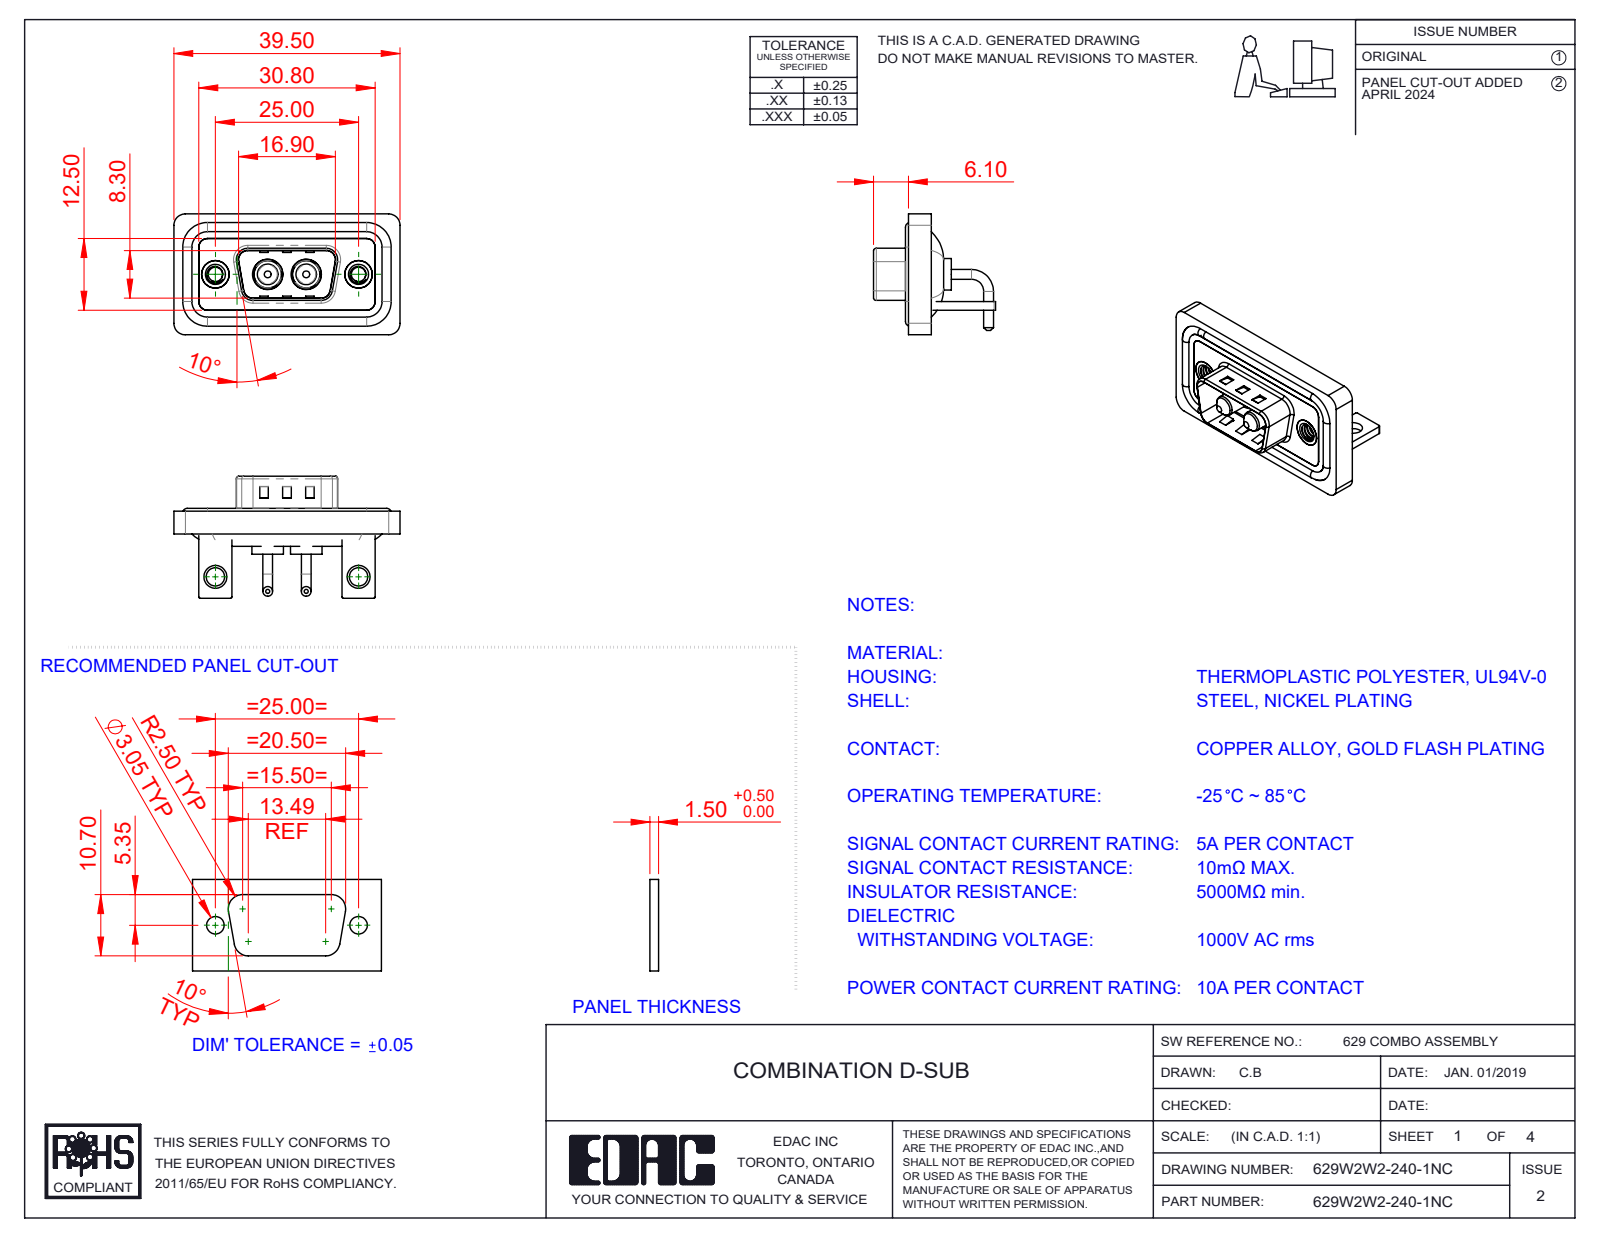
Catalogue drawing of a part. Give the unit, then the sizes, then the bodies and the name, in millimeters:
Units: millimetres
Overall size (bounding box): 39.5 × 21.3 × 21.1
Round holes (diameter × count): ⌀2.5 ×2, ⌀3.2 ×2, ⌀4 ×2, ⌀4.8 ×2, ⌀4.85 ×2, ⌀5 ×2, ⌀5.3 ×2
Round bosses / shafts (diameter × count): ⌀1.7 ×4, ⌀1.6 ×4, ⌀5.5 ×2, ⌀5.2 ×2, ⌀4.9 ×2, ⌀4.75 ×2, ⌀3.75 ×2, ⌀3.6 ×2
Partial cylindrical surfaces — rounded edges, fillets, slot ends (radius × count): R2 ×19, R1.5 ×18, R0.25 ×16, R0.5 ×9, R1.6 ×8, R0.6 ×4, R0.65 ×4, R0.9 ×4
Main face-to-face distances: 0.4, 1.5, 2.9, 0.8, 1.1, 1.2, 2.1, 1.6, 3.7, 2.5
Hole centre spacings: 9.14, 15.86, 25, 6.72
Volume: 4 740 mm³ · Surface area: 7 654 mm²
Bodies: 13 solids, 535 faces (185 planar, 240 cylindrical, 110 other)
Part name (STEP PRODUCT): 629Combo Threaded Rivet_B; Power Pin_10A RA; 629Combo Housing_2W2; 629Combo Stabilizer Bracket (+4 more)
STEP written by: SolidWorks 2023 (CONFIG_CONTROL_DESIGN)
